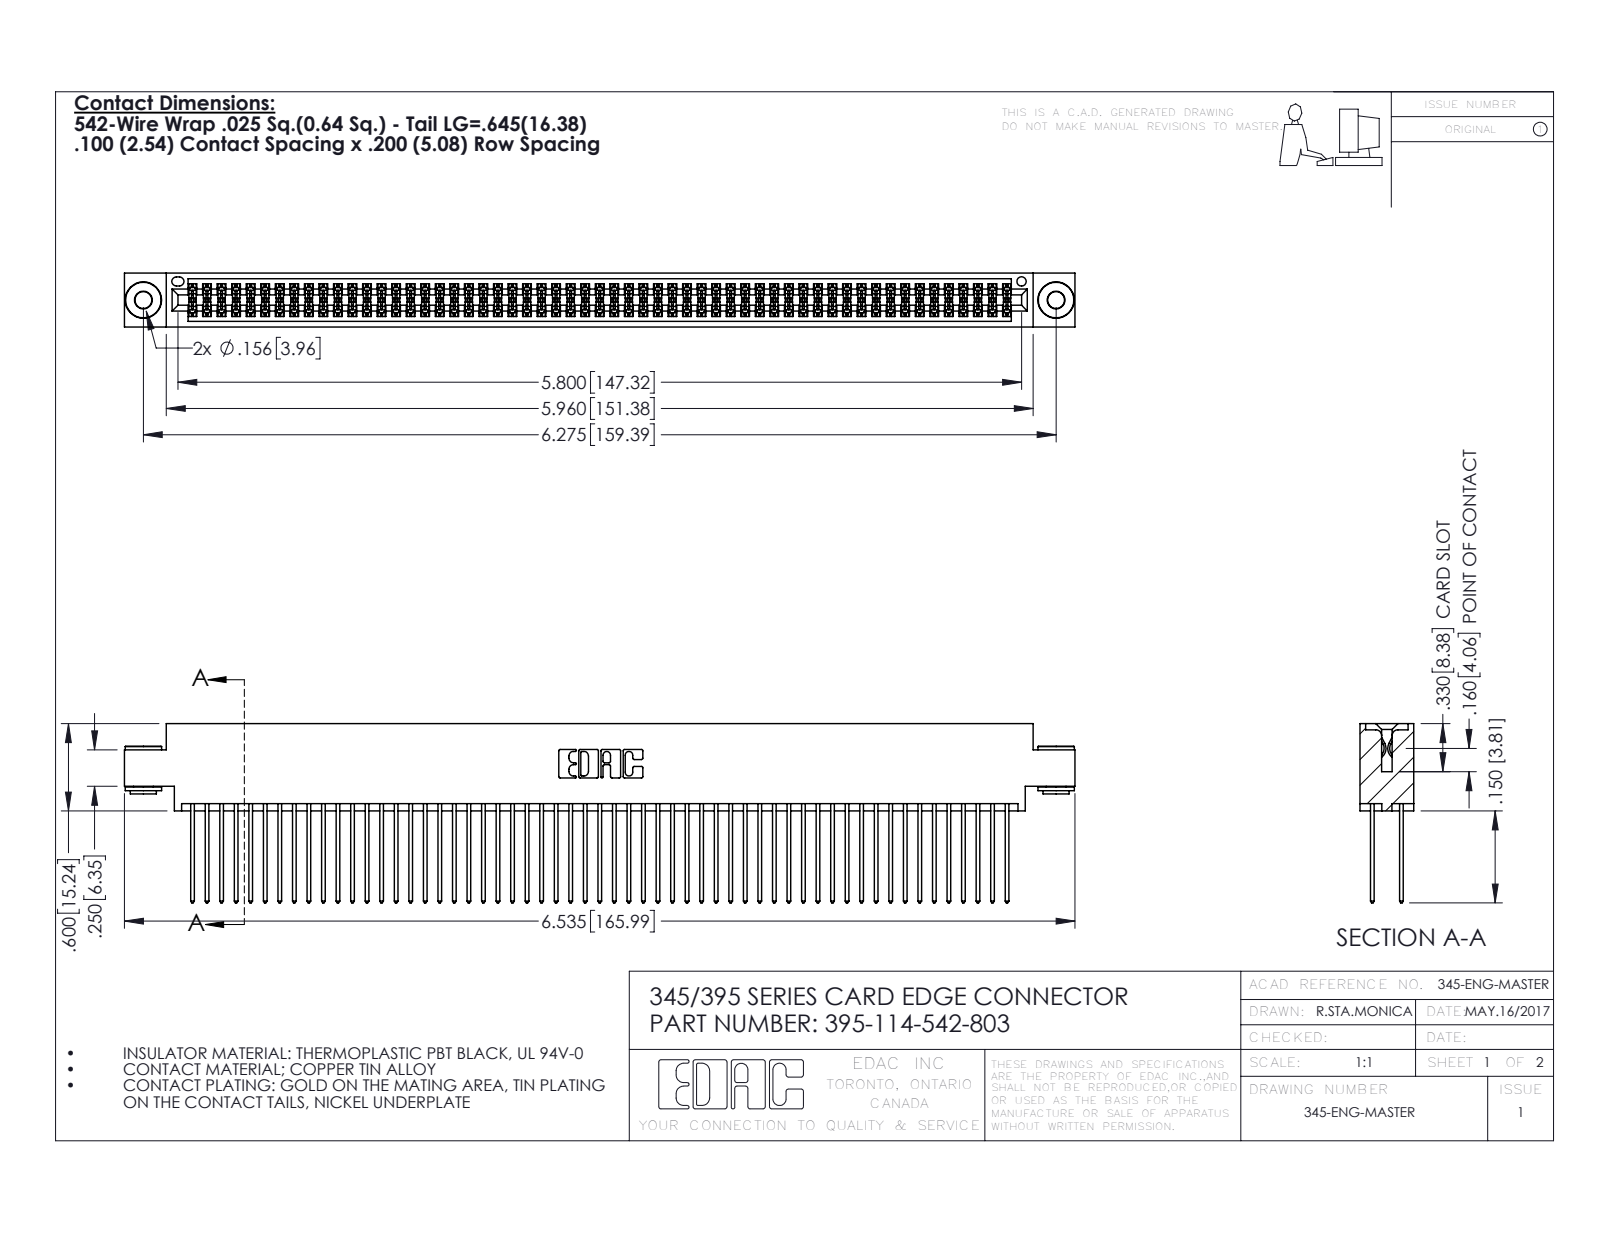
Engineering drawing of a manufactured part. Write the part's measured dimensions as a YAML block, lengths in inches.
part_name: "345 Part_0.170 Offset - 0.156 Dia-TH; 345-250-002_345-250-002-102; 345-292-001_345-293-142; 395-114-542-803"
step_written_by: "SolidWorks 2016 (CONFIG_CONTROL_DESIGN)"
units: inches
bodies: {solids: 117, faces: 5868, planar: 3856, cylindrical: 2004, other: 8}
overall_size: [6.535, 1.232, 0.37]
volume: 1.019
surface_area: 43.1
round_holes:
  - {diameter: 0.116, count: 2}
  - {diameter: 0.156, count: 2}
  - {diameter: 0.064, count: 1}
round_bosses_or_shafts:
  - {diameter: 0.25, count: 2}
  - {diameter: 0.18, count: 2}
  - {diameter: 0.136, count: 2}
partial_cylinders:
  - {radius: 0.006, count: 171}
  - {radius: 0.01, count: 114}
  - {radius: 0.01, count: 22}
  - {radius: 0.007, count: 6}
  - {radius: 0.031, count: 6}
  - {radius: 0.026, count: 3}
  - {radius: 0.014, count: 2}
  - {radius: 0.019, count: 2}
face_to_face_distances: [0.072, 0.298, 0.2, 0.098, 0.272, 0.025, 0.37, 0.225, 0.175, 0.149]
hole_center_spacings: [0.27, 6.039, 6.275]
